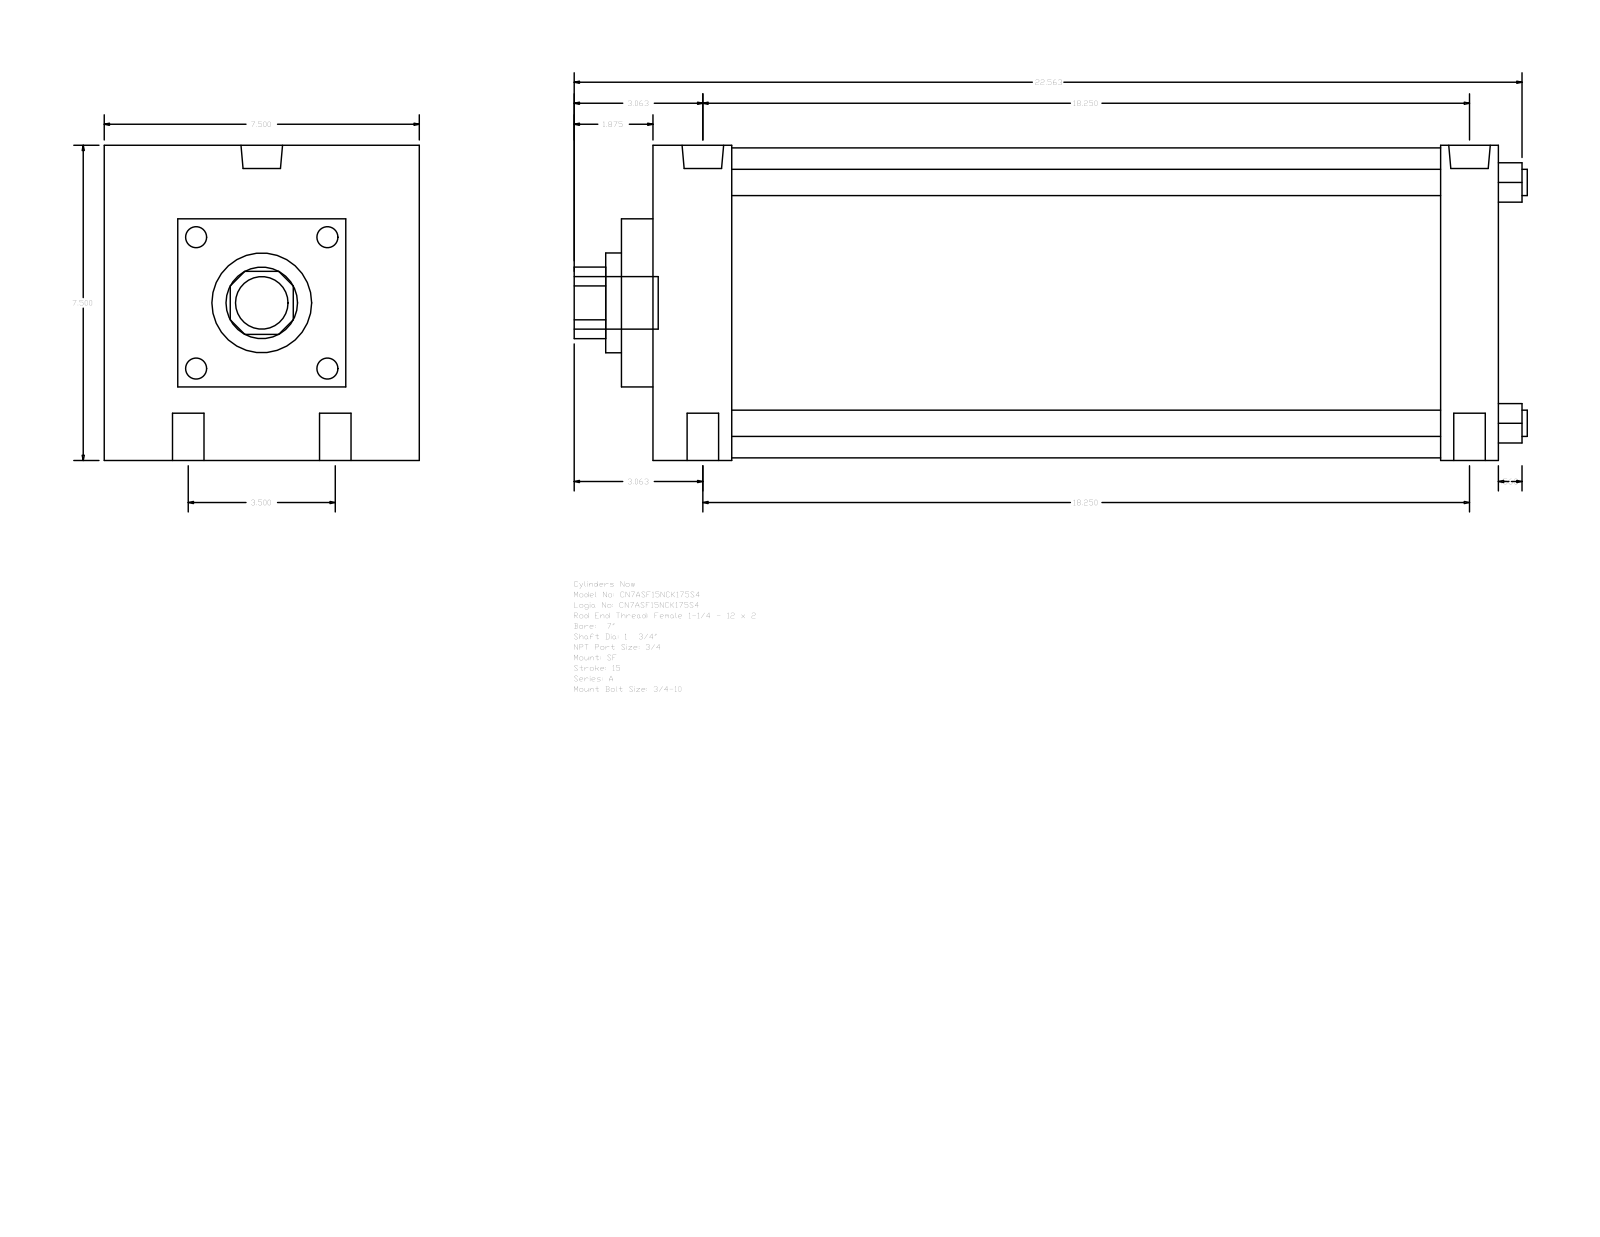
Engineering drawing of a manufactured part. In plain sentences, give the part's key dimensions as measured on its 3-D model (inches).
The part is named "A_SF__0700_1.75". Its 3-D file was written by "GSSL Pune (CONFIG_CONTROL_DESIGN)". It is 0 solids with 93 faces: 67 planar, 26 cylindrical and 0 other. Overall it measures 22.687 by 7.5 by 7.5 inches. Round holes: 4 of diameter 0.75, 2 of diameter 0.594, 2 of diameter 0.989, 1 of diameter 1.75, 1 of diameter 2.375. Round bosses or shafts: 4 of diameter 0.625, 1 of diameter 7.375, 1 of diameter 1.25. Partial cylindrical surfaces (rounded edges, fillets, slot ends): 1 of radius 0.852. The main face-to-face distances are 7.5, 20.125, 1.75, 1.375, 0.75, 1.875, 18.75, 16.875, 18.25, 5.75. The hole center spacings are 1.75, 18.334, 18.25, 3.5, 18.583, 17.812.
